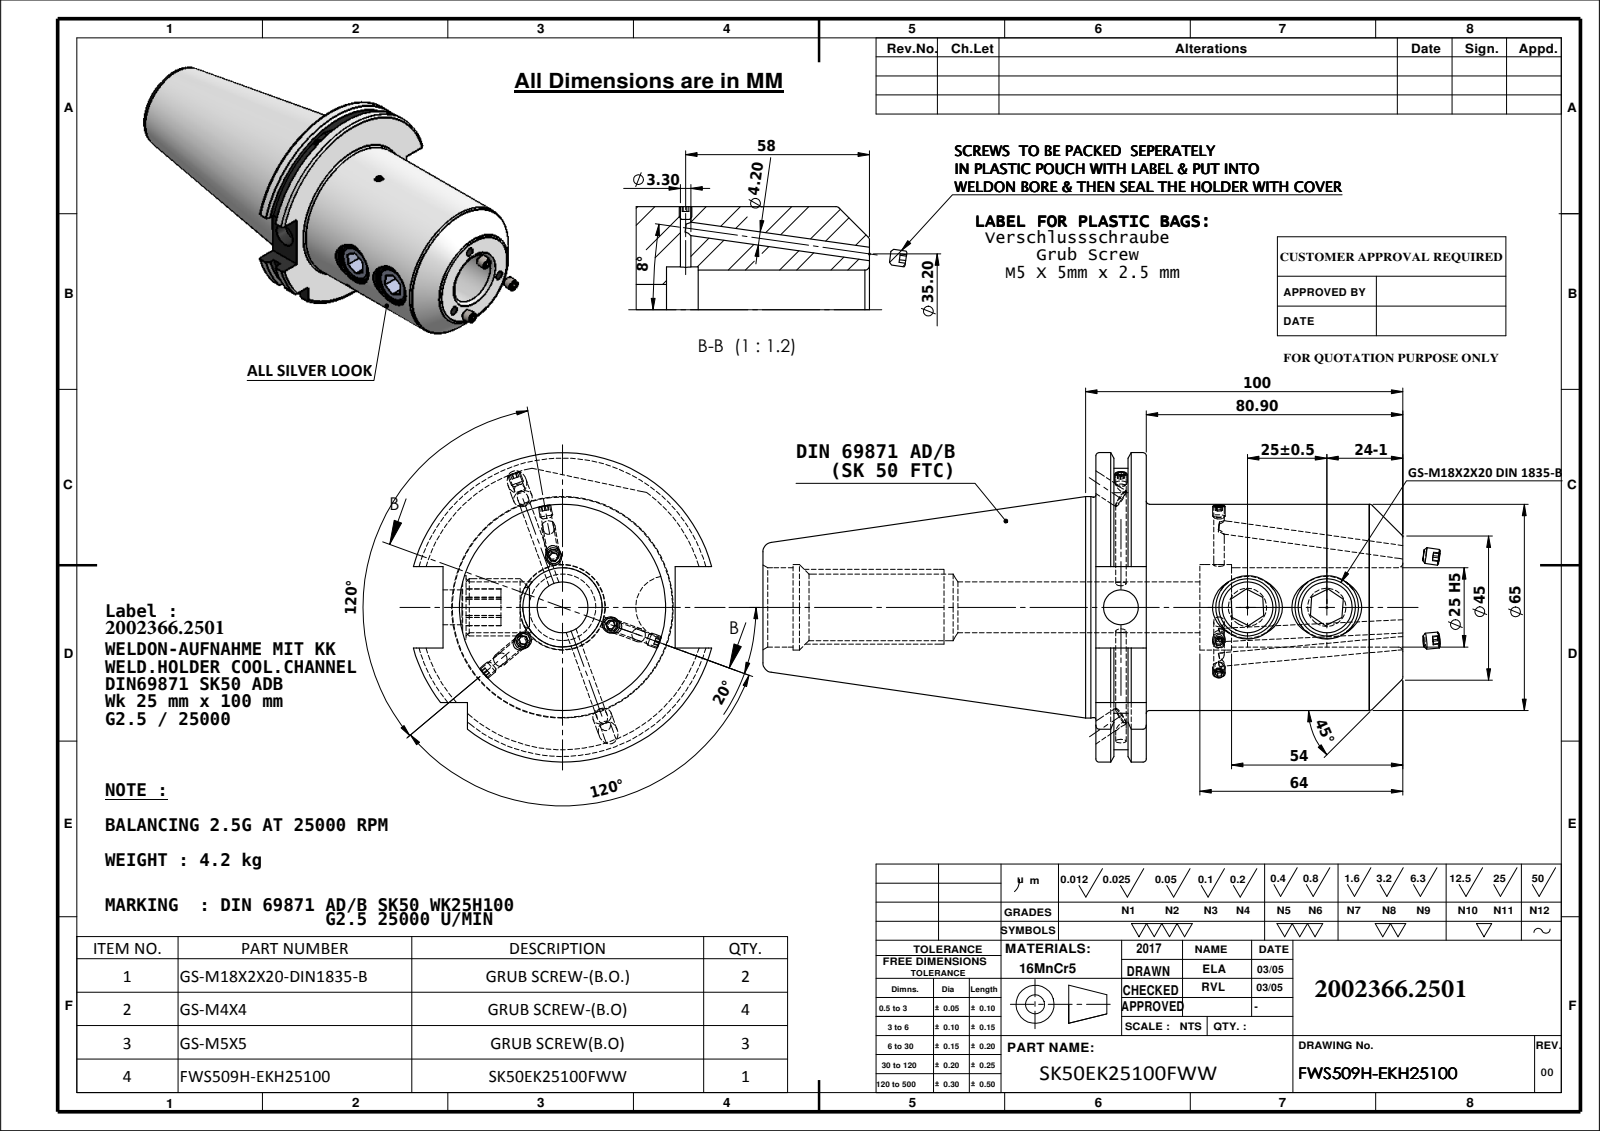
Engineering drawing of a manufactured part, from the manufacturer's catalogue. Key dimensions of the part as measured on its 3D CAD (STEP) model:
Part name (STEP PRODUCT): 91506-WK225100; SK50EK25100FWW; GS-M18X2X20; M5X5_DIN 913 - M5 x 5-N (+1 more)
STEP written by: SolidWorks 2009 (CONFIG_CONTROL_DESIGN)
Units: millimetres
Bodies: 10 solids, 290 faces (114 planar, 86 cylindrical, 90 other)
Overall size (bounding box): 213.5 × 97.5 × 94.05
Volume: 543 173 mm³ · Surface area: 74 099 mm²
Round holes (diameter × count): ⌀3.3 ×4, ⌀4.2 ×3, ⌀16 ×3, ⌀6 ×2, ⌀20 ×2, ⌀11 ×1, ⌀21 ×1, ⌀25 ×1, ⌀27 ×1
Round bosses / shafts (diameter × count): ⌀4 ×4, ⌀5 ×3, ⌀18 ×2, ⌀69.85 ×1, ⌀69.45 ×1, ⌀65 ×1
Partial cylindrical surfaces — rounded edges, fillets, slot ends (radius × count): R44.9 ×1, R48.75 ×1
Main face-to-face distances: 15.9, 96.8, 80.9, 10.15, 5.75, 86.65, 5.66, 4.49, 10.24, 91.14
Hole centre spacings: 25, 39.9, 64.9
